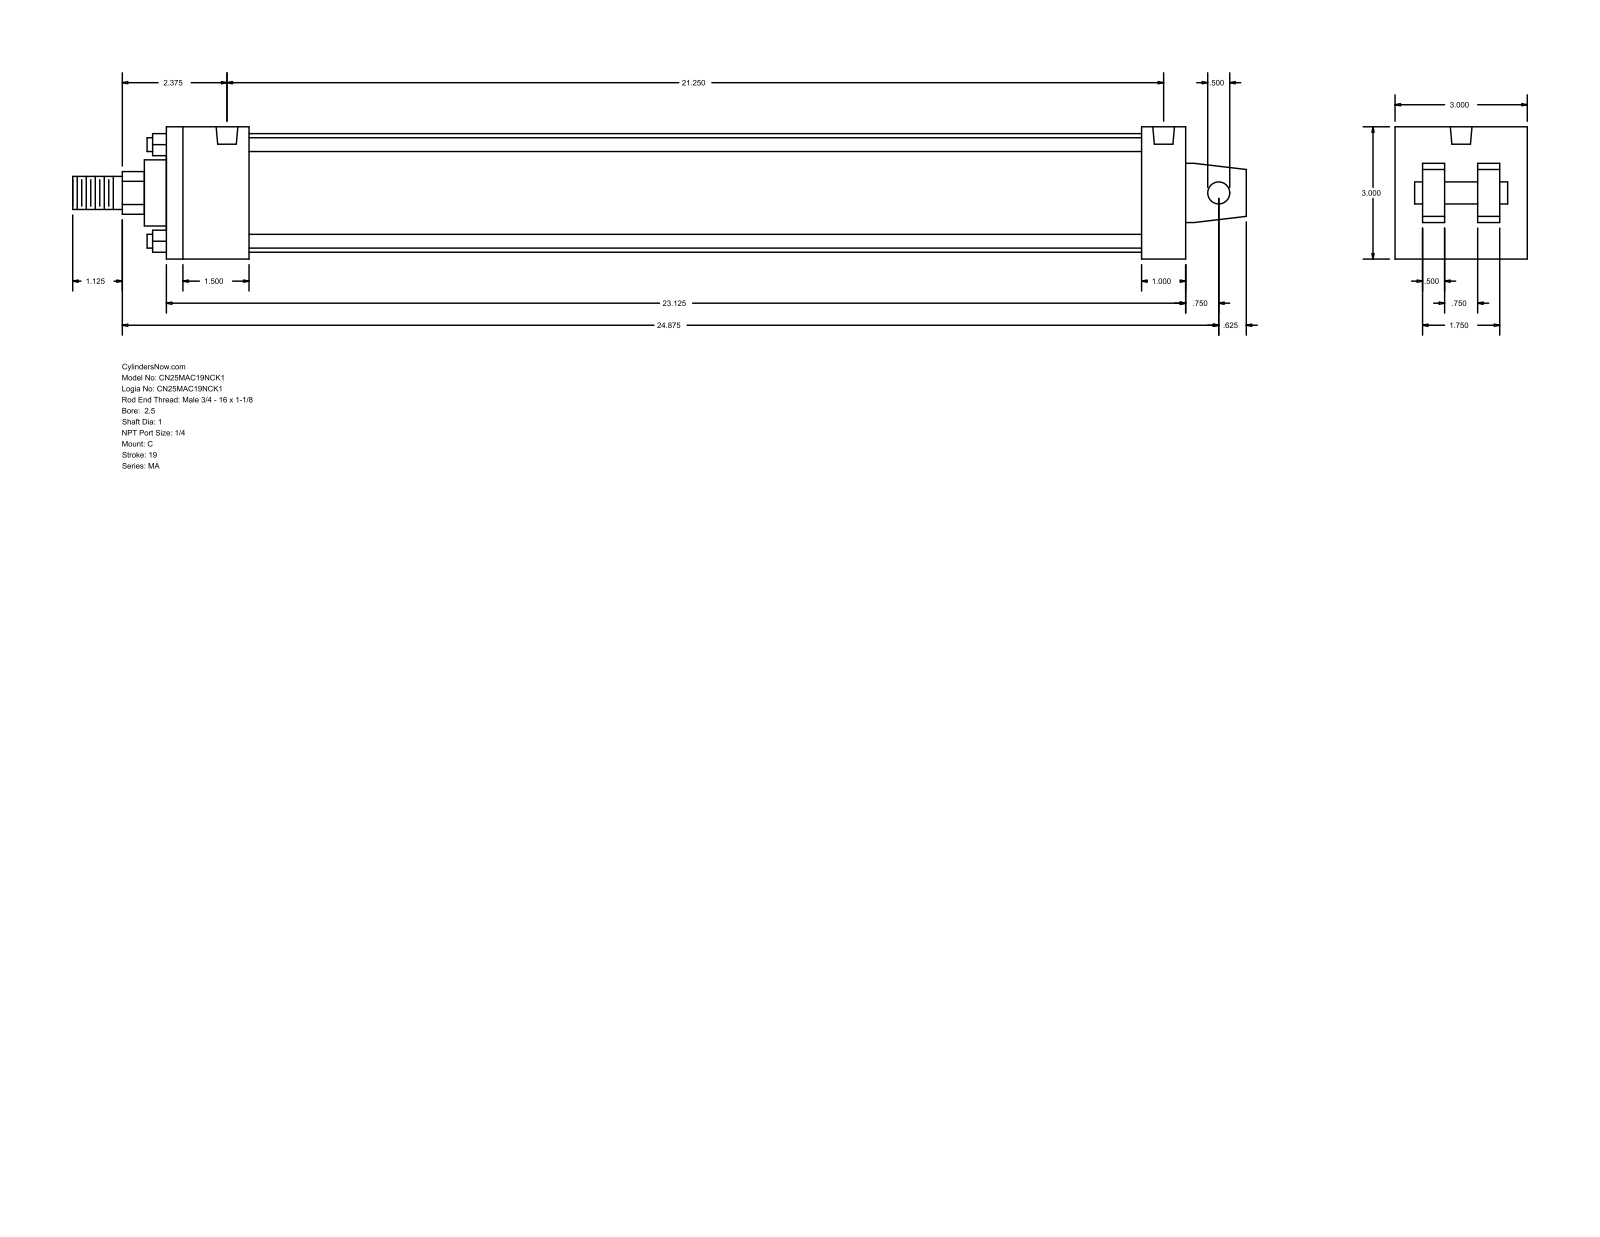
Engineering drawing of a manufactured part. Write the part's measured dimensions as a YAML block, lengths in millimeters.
part_name: "MA_C__0250_1"
step_written_by: "GSSL Pune (CONFIG_CONTROL_DESIGN)"
units: millimeters
bodies: {solids: 0, faces: 103, planar: 76, cylindrical: 27, other: 0}
overall_size: [676.27, 76.2, 76.2]
round_holes:
  - {diameter: 7.94, count: 4}
  - {diameter: 12.49, count: 2}
round_bosses_or_shafts:
  - {diameter: 7.94, count: 4}
  - {diameter: 68.33, count: 1}
  - {diameter: 38.1, count: 1}
  - {diameter: 25.4, count: 1}
  - {diameter: 19.05, count: 1}
  - {diameter: 12.7, count: 1}
partial_cylinders:
  - {radius: 12.29, count: 1}
face_to_face_distances: [76.2, 47.63, 587.37, 12.7, 60.33, 15.87, 28.57, 561.98, 514.35, 539.74]
hole_center_spacings: [539.75]
